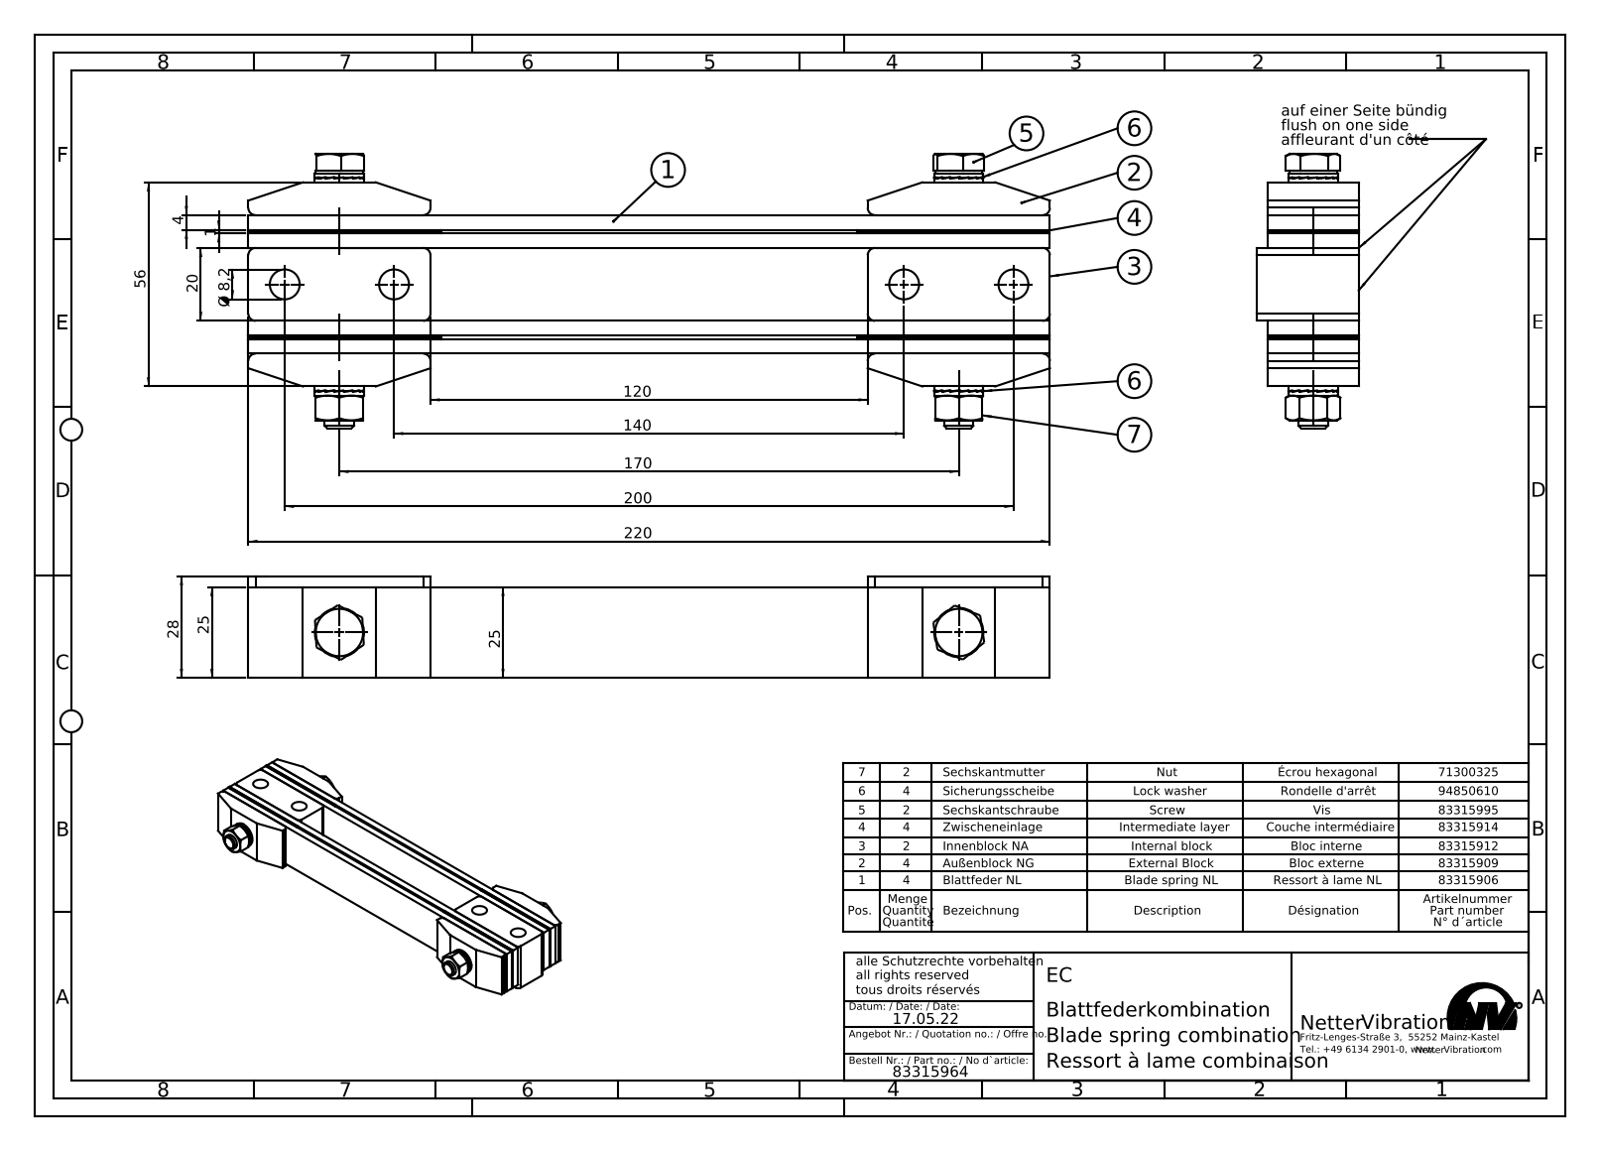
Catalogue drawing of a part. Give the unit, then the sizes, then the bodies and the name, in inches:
Units: inches
Overall size (bounding box): 8.661 × 2.965 × 1.102
Round holes (diameter × count): ⌀0.323 ×6, ⌀0.268 ×2, ⌀0.315 ×2, ⌀0.335 ×2, ⌀0.343 ×2
Round bosses / shafts (diameter × count): ⌀0.531 ×2, ⌀0.512 ×2
Partial cylindrical surfaces — rounded edges, fillets, slot ends (radius × count): R0.079 ×16
Main face-to-face distances: 1.142, 0.157, 0.197, 0.984, 0.354, 0.039, 0.945, 1.299, 1.339, 1.102
Hole centre spacings: 6.693, 1.181, 5.512, 7.874
Volume: 11.31 in³ · Surface area: 153.8 in²
Bodies: 22 solids, 746 faces (594 planar, 100 cylindrical, 52 other)
Part name (STEP PRODUCT): Blattfederkombination EC # 83315964
STEP written by: SolidWorks 2015 (AUTOMOTIVE_DESIGN)
